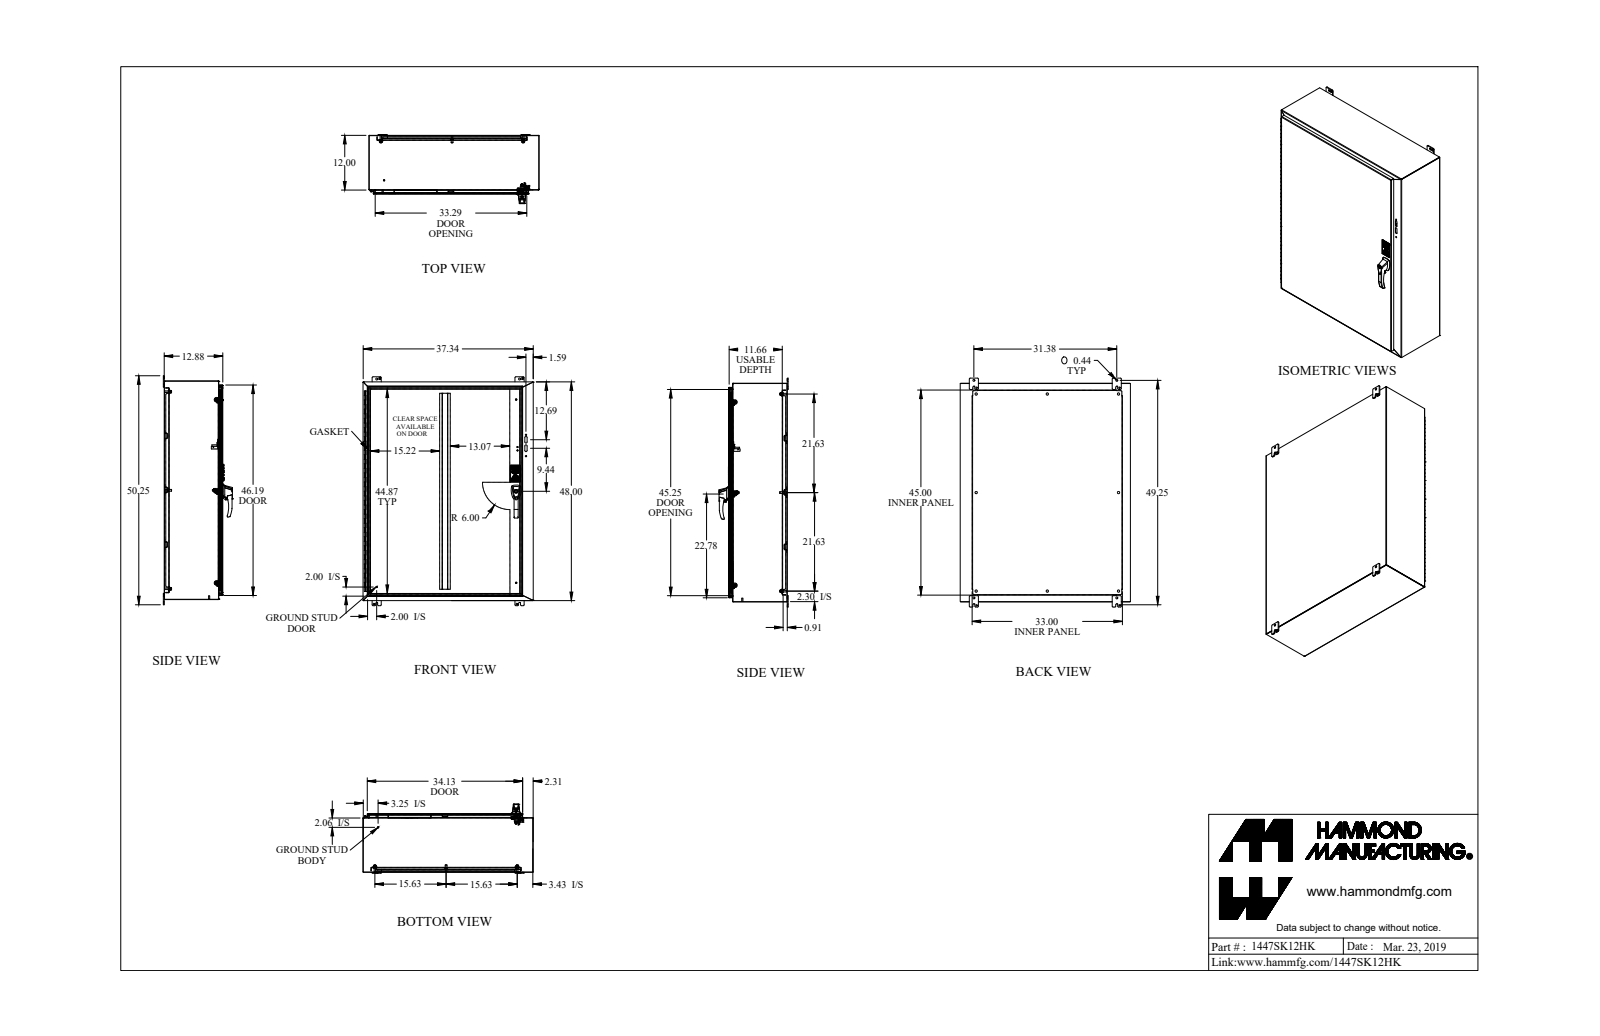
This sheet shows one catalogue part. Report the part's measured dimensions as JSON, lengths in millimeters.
{"part_name": "1447SK12HK_Default", "step_written_by": "SolidWorks 2019 (CONFIG_CONTROL_DESIGN)", "units": "millimeters", "bodies": {"solids": 71, "faces": 2066, "planar": 1036, "cylindrical": 828, "other": 202}, "overall_size": [1276.4, 949.3, 385.5], "volume_mm3": 10680000, "surface_area_mm2": 10790000, "round_holes": [[12.7, 8], [4.5, 6], [8, 6], [7.8, 4], [11.1, 4], [11.3, 4], [6.4, 3], [6.7, 3], [10.5, 3], [4, 2], [4.4, 2], [5, 2]], "round_bosses_or_shafts": [[9.5, 11], [6.4, 9], [16.5, 8], [8.4, 8], [25.4, 7], [4, 6], [9.5, 3], [16, 2]], "partial_cylinders_radius": [[4.8, 35], [6.4, 35], [0.9, 18], [2.7, 18], [2.9, 16], [3.2, 16], [0.8, 10], [5.5, 8]], "face_to_face_distances": [1.8, 325.2, 323.4, 327, 2.4, 299, 297.2, 26.2, 28, 301.4], "hole_center_spacings": [793.8, 965.3, 1355.3, 44.1, 396.9, 549.3, 788.3, 796.9]}
